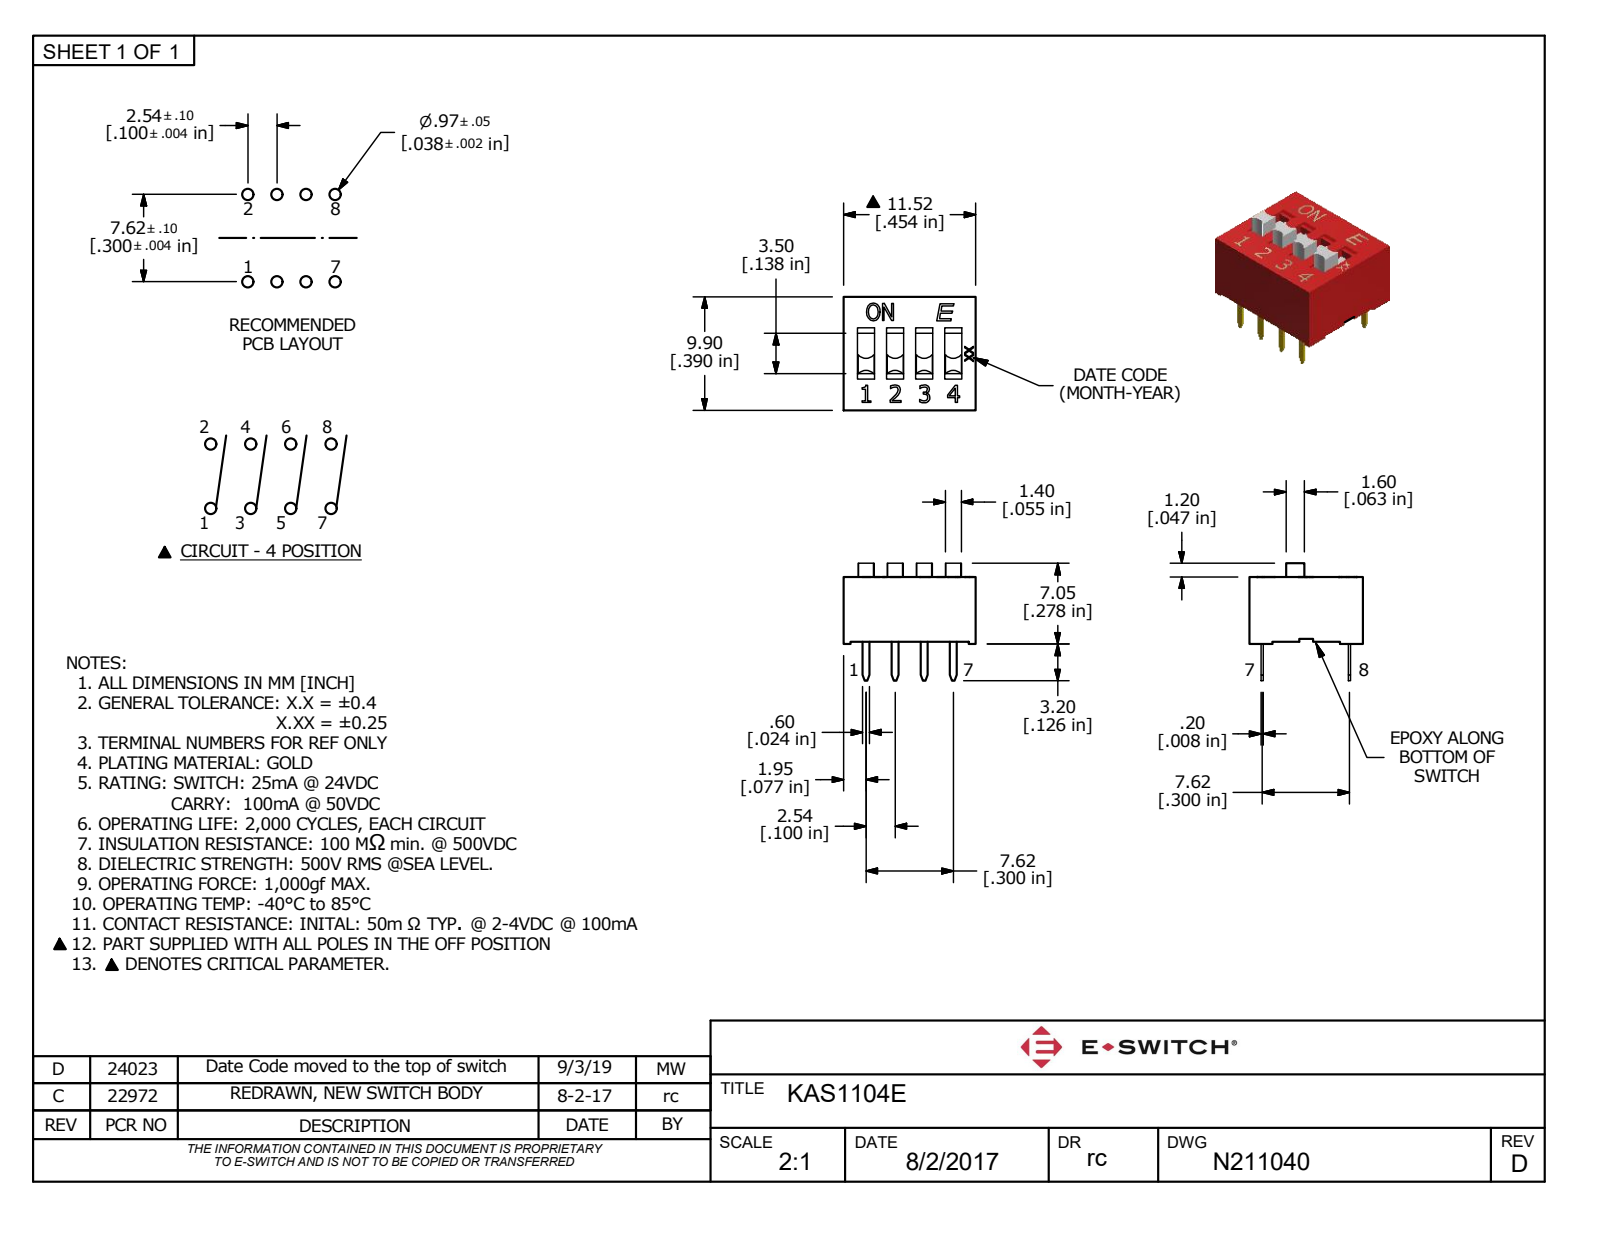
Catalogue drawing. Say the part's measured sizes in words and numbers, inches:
The part is named "P:\\\\E-Switch Secure\\\\3D_MODELS_STP_FORMAT\\\\KAS1104E.stp". Its 3-D file was written by "ACIS (CONFIG_CONTROL_DESIGN)". It is 1 solid with 142 faces: 134 planar, 8 cylindrical and 0 other. Overall it measures 0.454 by 0.402 by 0.39 inches. Its volume is 0.035 cubic inches and its surface area 1.008 square inches. Partial cylindrical surfaces (rounded edges, fillets, slot ends): 8 of radius 0.035. The main face-to-face distances are 0.194, 0.39, 0.454, 0.1, 0.3, 0.126, 0.264, 0.024, 0.234, 0.042.
